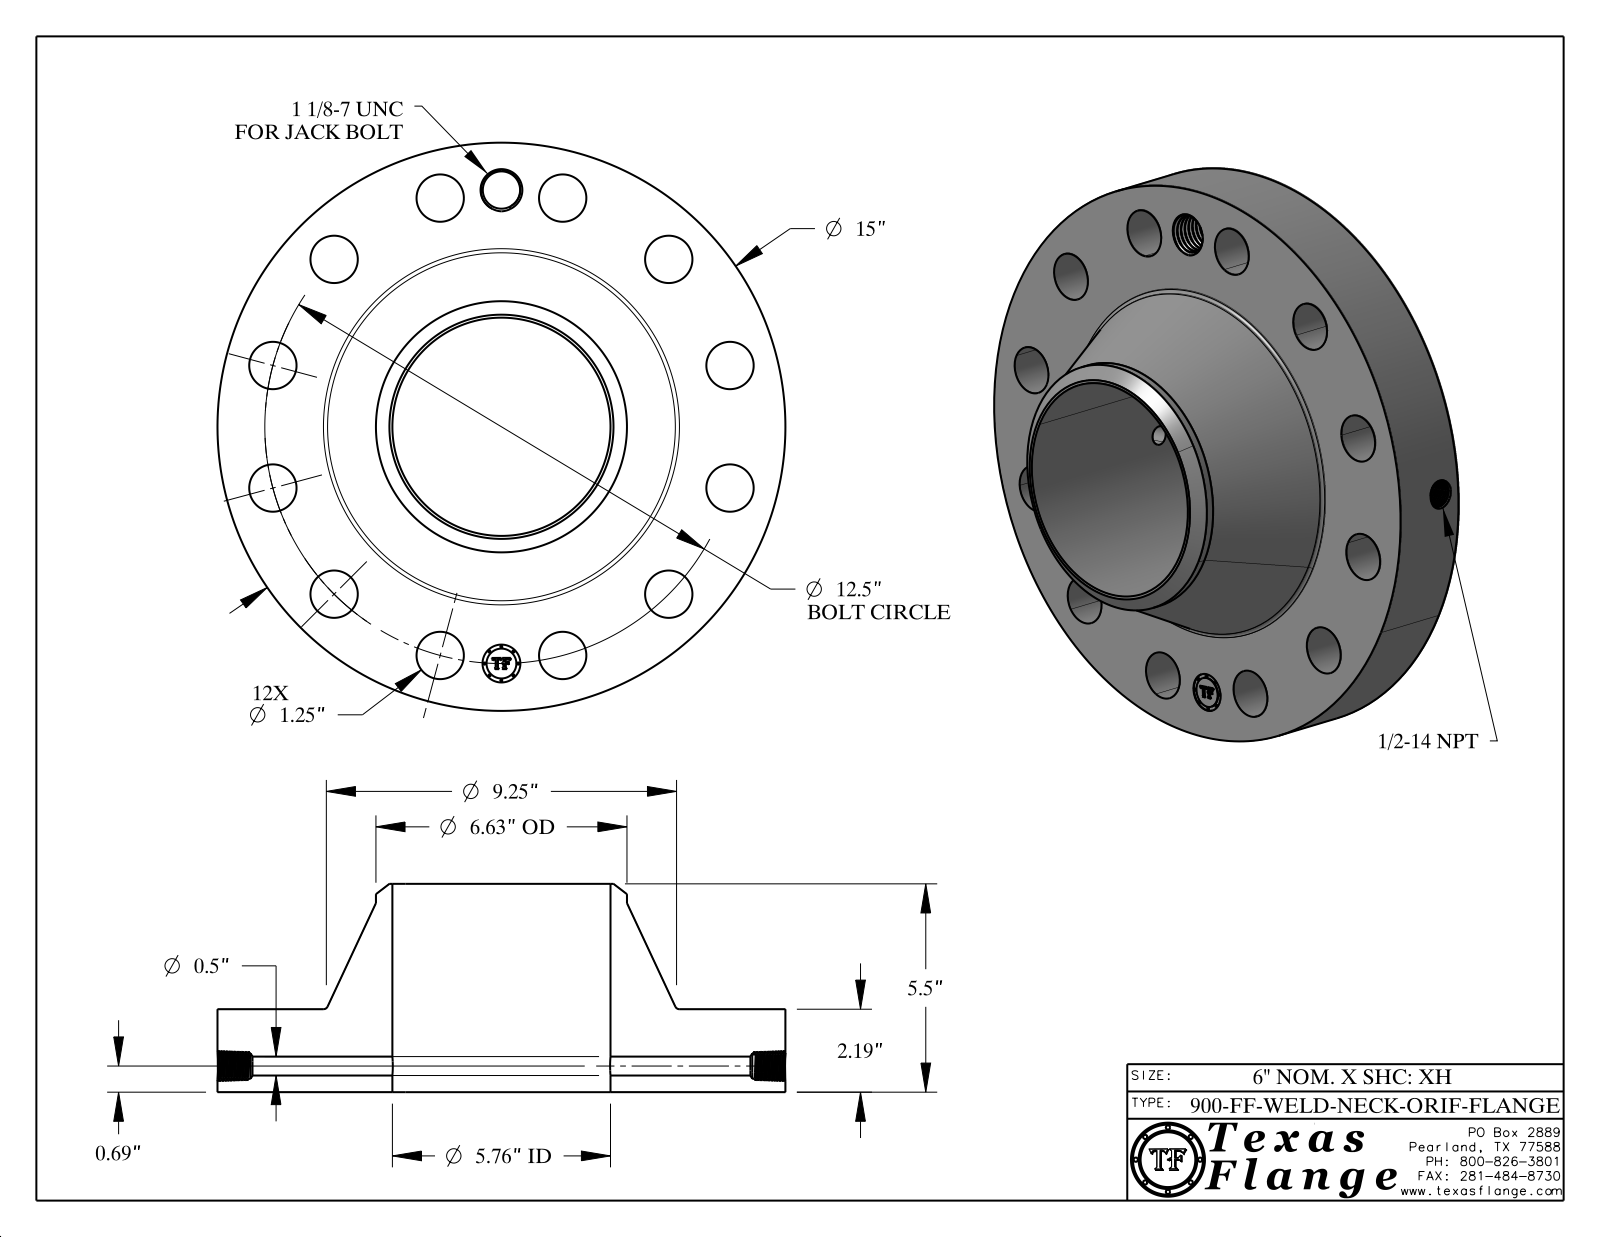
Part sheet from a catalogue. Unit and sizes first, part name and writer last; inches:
Units: inches
Overall size (bounding box): 15 × 15 × 5.5
Round holes (diameter × count): ⌀1.25 ×12, ⌀0.5 ×1, ⌀0.672 ×1, ⌀0.984 ×1, ⌀1 ×1, ⌀5.761 ×1
Round bosses / shafts (diameter × count): ⌀0.061 ×8, ⌀15 ×1, ⌀6.63 ×1, ⌀0.788 ×1
Main face-to-face distances: 2.19, 5.5, 3.31, 2.175, 0.015, 3.325, 0.298, 0.293, 0.054, 0.248
Hole centre spacings: 6.25, 12.074, 3.235, 8.839, 10.825, 12.5, 1.631, 3.235
Volume: 363.8 in³ · Surface area: 654.9 in²
Bodies: 1 solid, 777 faces (368 planar, 100 cylindrical, 309 other)
Part name (STEP PRODUCT): 900-FF-WELD-NECK
STEP written by: CATIA V5 STEP AP214 (AUTOMOTIVE_DESIGN)
